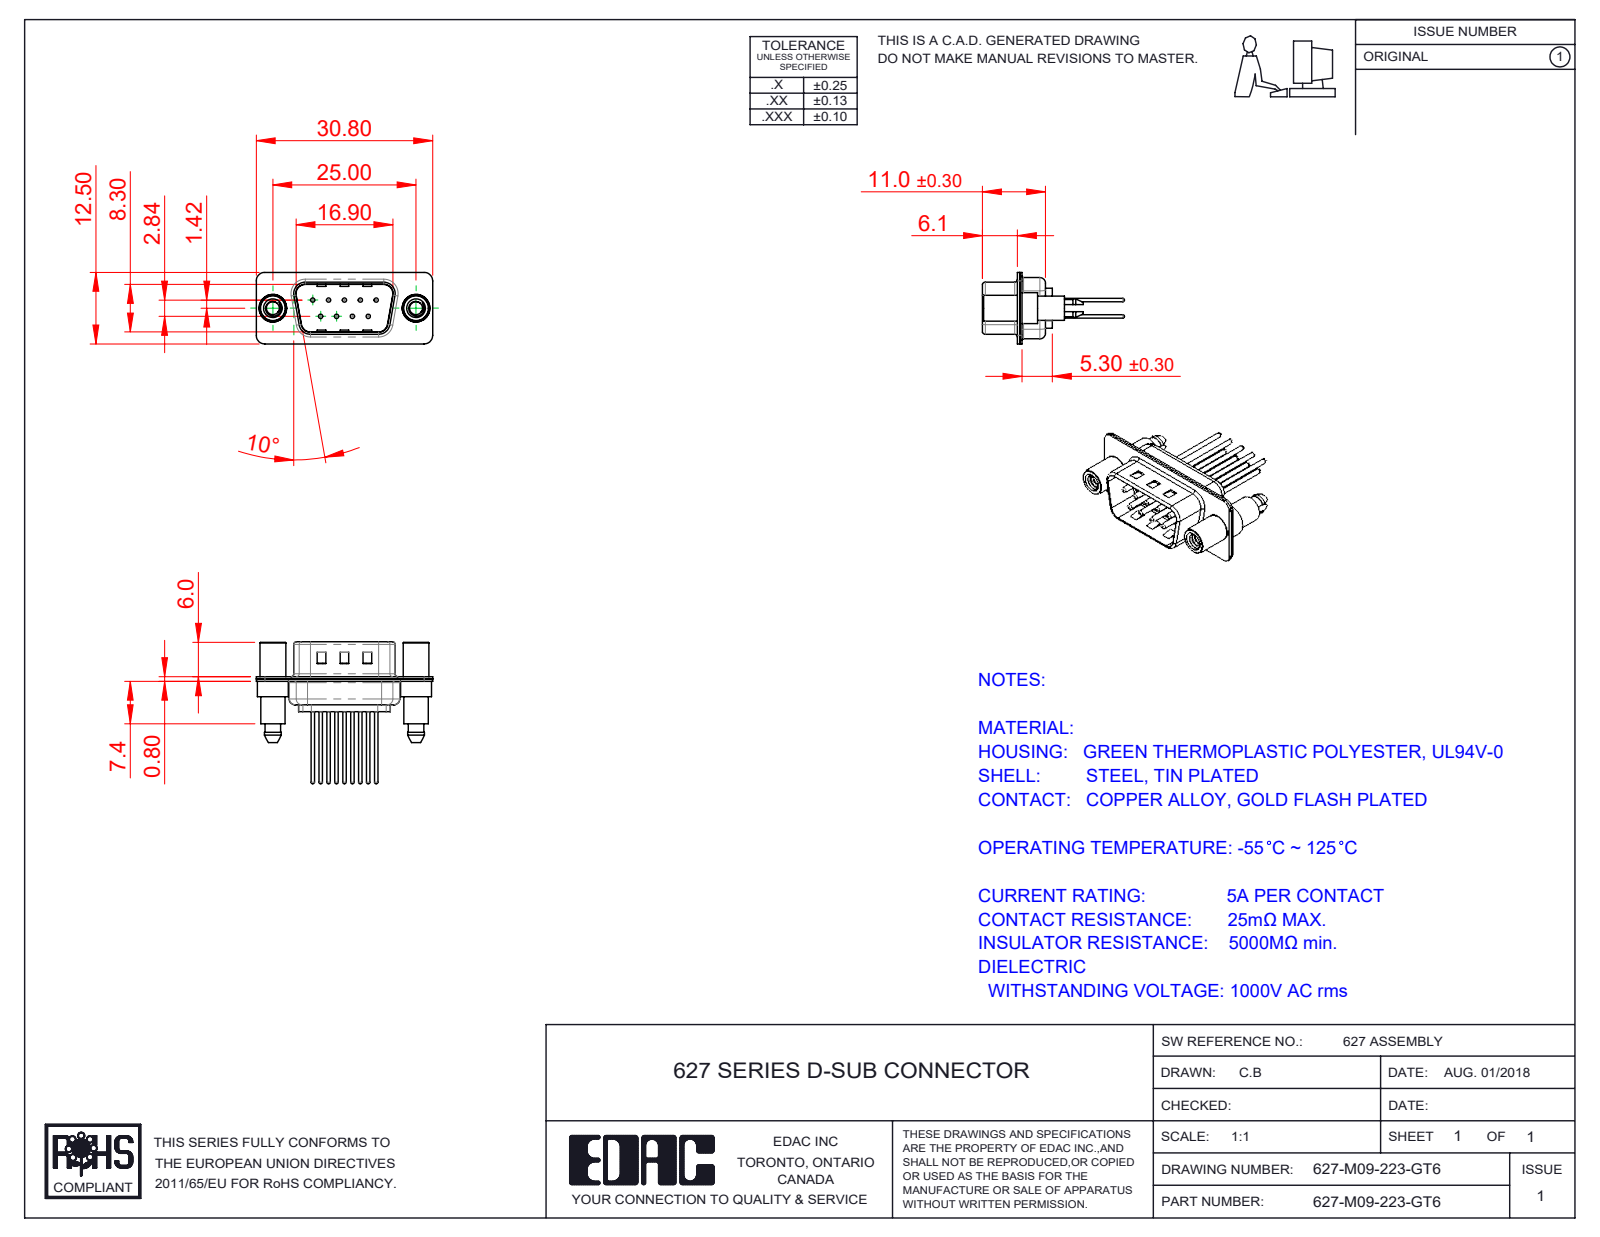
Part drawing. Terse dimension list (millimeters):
name: 627M Contact Row 1_23; 627M 4-40 Threaded Standoff and Boardlock; 627M Contact Row 2_23; 627M Housing_09 Contacts (+3 more)
written by: SolidWorks 2020 (CONFIG_CONTROL_DESIGN)
unit: mm
bodies: 14 solids, 689 faces (188 planar, 283 cylindrical, 218 other)
size: 30.8 × 24.77 × 12.5
volume: 1 666 mm³; area: 4 158 mm²
holes: 9× ⌀0.75, 9× ⌀1.6, 9× ⌀2, 2× ⌀2.26, 2× ⌀4, 2× ⌀4.8
bosses: 9× ⌀1.5, 9× ⌀0.6, 2× ⌀5.4, 2× ⌀4.9, 2× ⌀4.5, 2× ⌀4.25
rounds: 18× R1.5, 12× R2, 10× R1.6, 8× R0.5, 4× R0.25, 4× R0.6, 4× R0.65, 4× R0.9
face distances: 0.4, 0.8, 9.5, 9.1, 8.7, 0.65, 9.9, 1.2, 5.3, 6.1
hole spacings: 3.16, 2.77, 5.54, 5.03, 5.04, 8.31, 7.1, 7.48
